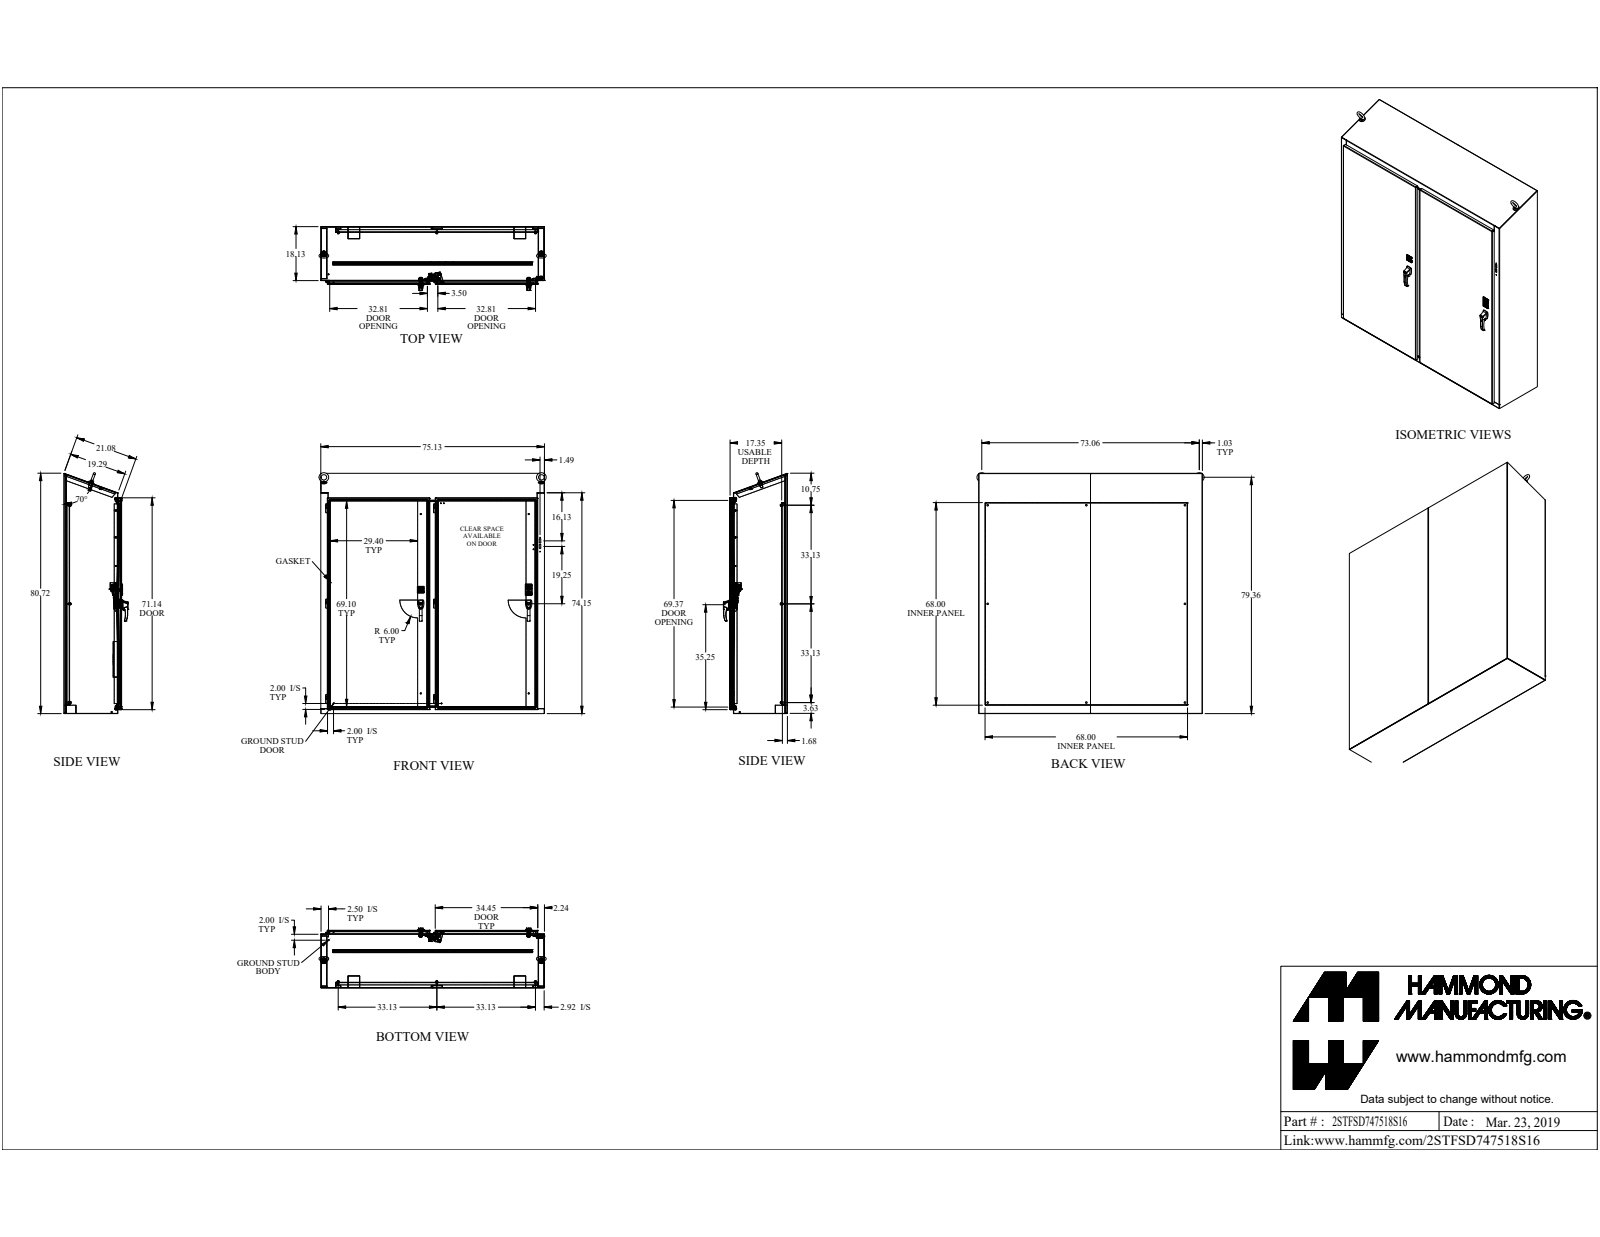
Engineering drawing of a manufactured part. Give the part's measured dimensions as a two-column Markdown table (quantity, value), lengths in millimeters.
| quantity | value |
| --- | --- |
| part name | 2STFSD747518S16 |
| STEP written by | SolidWorks 2019 (CONFIG_CONTROL_DESIGN) |
| units | millimeters |
| bodies | 210 solids, 3274 faces (1902 planar, 992 cylindrical, 380 other) |
| overall size | 2054.5 × 1938.2 × 545.9 |
| volume | 43 260 000 mm³ |
| surface area | 33 920 000 mm² |
| round holes (diameter × count) | 5 × 11, 7.1 × 9, 7.8 × 9, 8.9 × 8, 14.3 × 8, 6.4 × 7, 8 × 6, 11.3 × 6, 6.5 × 4, 7.2 × 4, 9.5 × 4, 9.9 × 4 |
| round bosses / shafts (diameter × count) | 6.4 × 18, 25.4 × 12, 16.5 × 9, 9.5 × 9, 8.4 × 8, 19.1 × 6, 15.9 × 5, 12.7 × 5 |
| partial cylindrical surfaces (radius × count) | 3.2 × 66, 1.2 × 36, 3.6 × 36, 12.7 × 34, 0.8 × 28, 1.5 × 27, 6.4 × 24, 0.3 × 20 |
| main face-to-face distances | 2.4, 2.4, 489.1, 3.2, 46, 48.4, 42.8, 45.3, 1905.8, 0.6 |
| hole center spacings | 1855.7, 1881.4, 1682.8, 841.4, 841.4, 756.1, 819, 920.9 |
